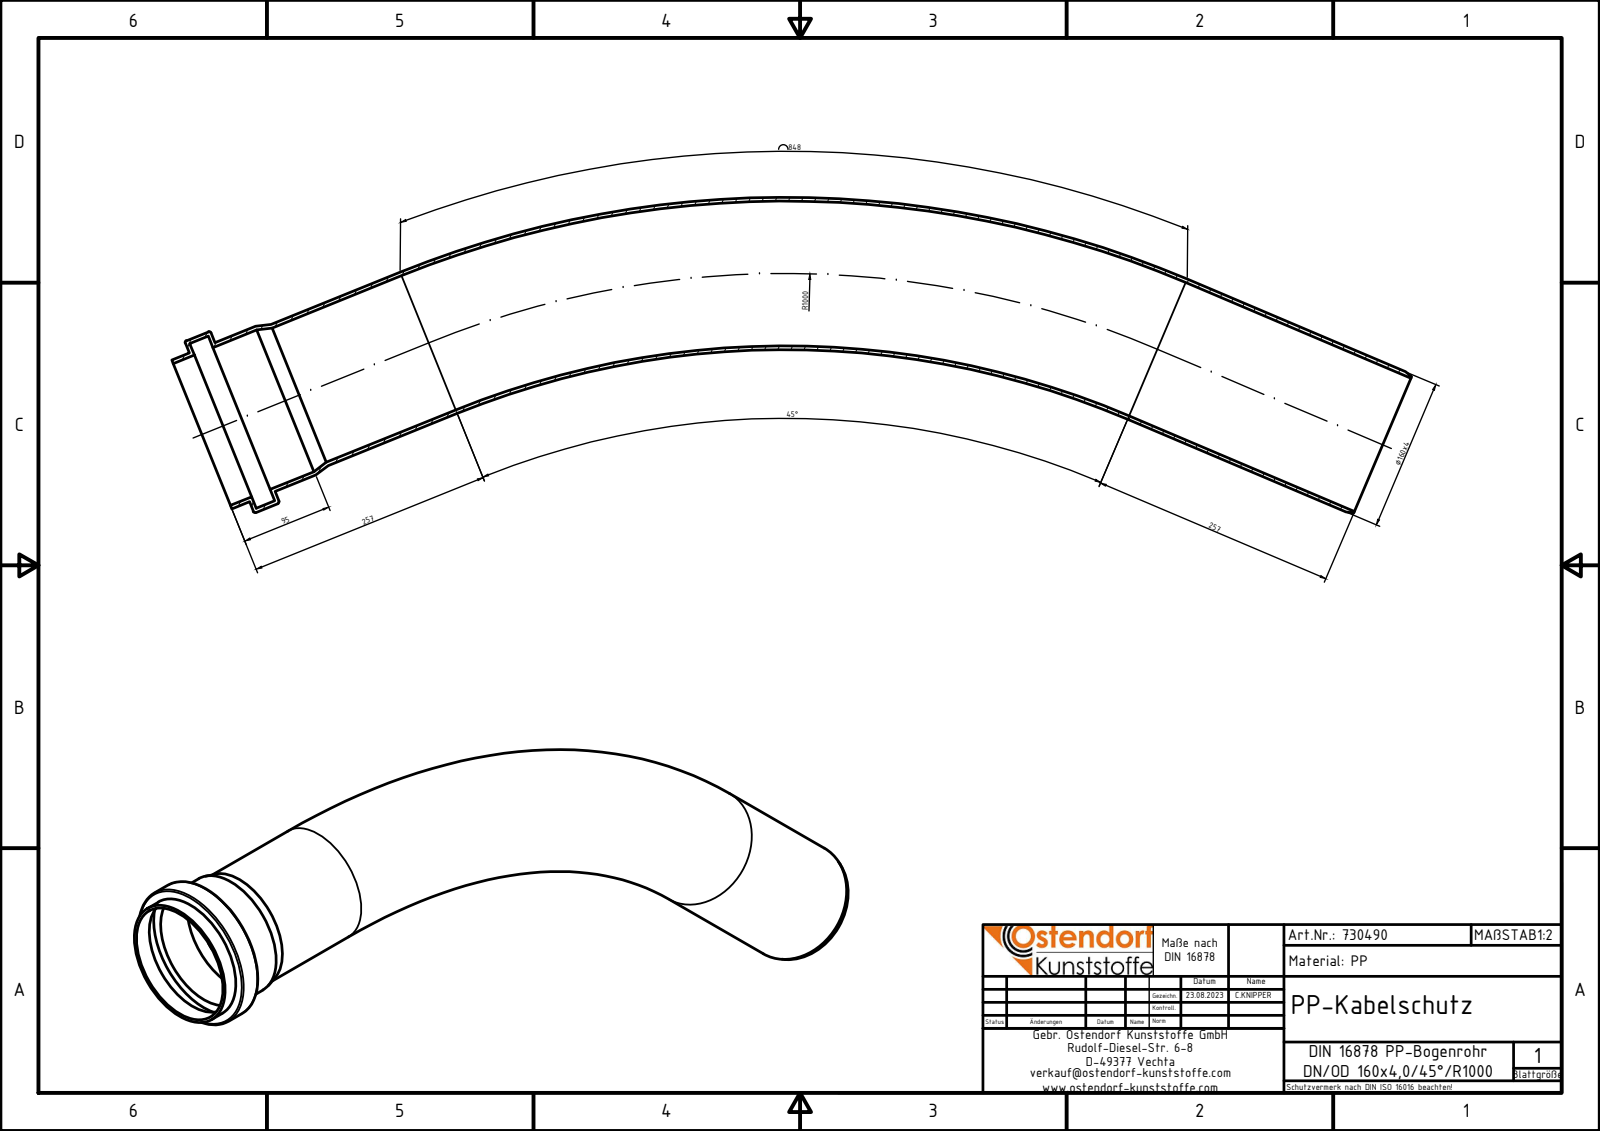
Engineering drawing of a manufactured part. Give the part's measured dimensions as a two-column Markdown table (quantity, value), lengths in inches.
| quantity | value |
| --- | --- |
| part name | PP-Bogenrohr_160x40_R1000_45_SM__34867_730490 |
| STEP written by | Autodesk Inventor 2024 (AUTOMOTIVE_DESIGN) |
| units | inches |
| bodies | 1 solid, 23 faces (6 planar, 10 cylindrical, 7 other) |
| overall size | 47.279 × 24.682 × 7.657 |
| volume | 159.9 in³ |
| surface area | 2 038 in² |
| round holes (diameter × count) | 5.984 × 2, 6.319 × 1, 7.343 × 1 |
| round bosses / shafts (diameter × count) | 6.299 × 2, 7.657 × 1, 6.634 × 1 |
| main face-to-face distances | 0.157, 0.984, 0.827, 1.142, 0.787, 0.945, 1.772, 1.929 |
